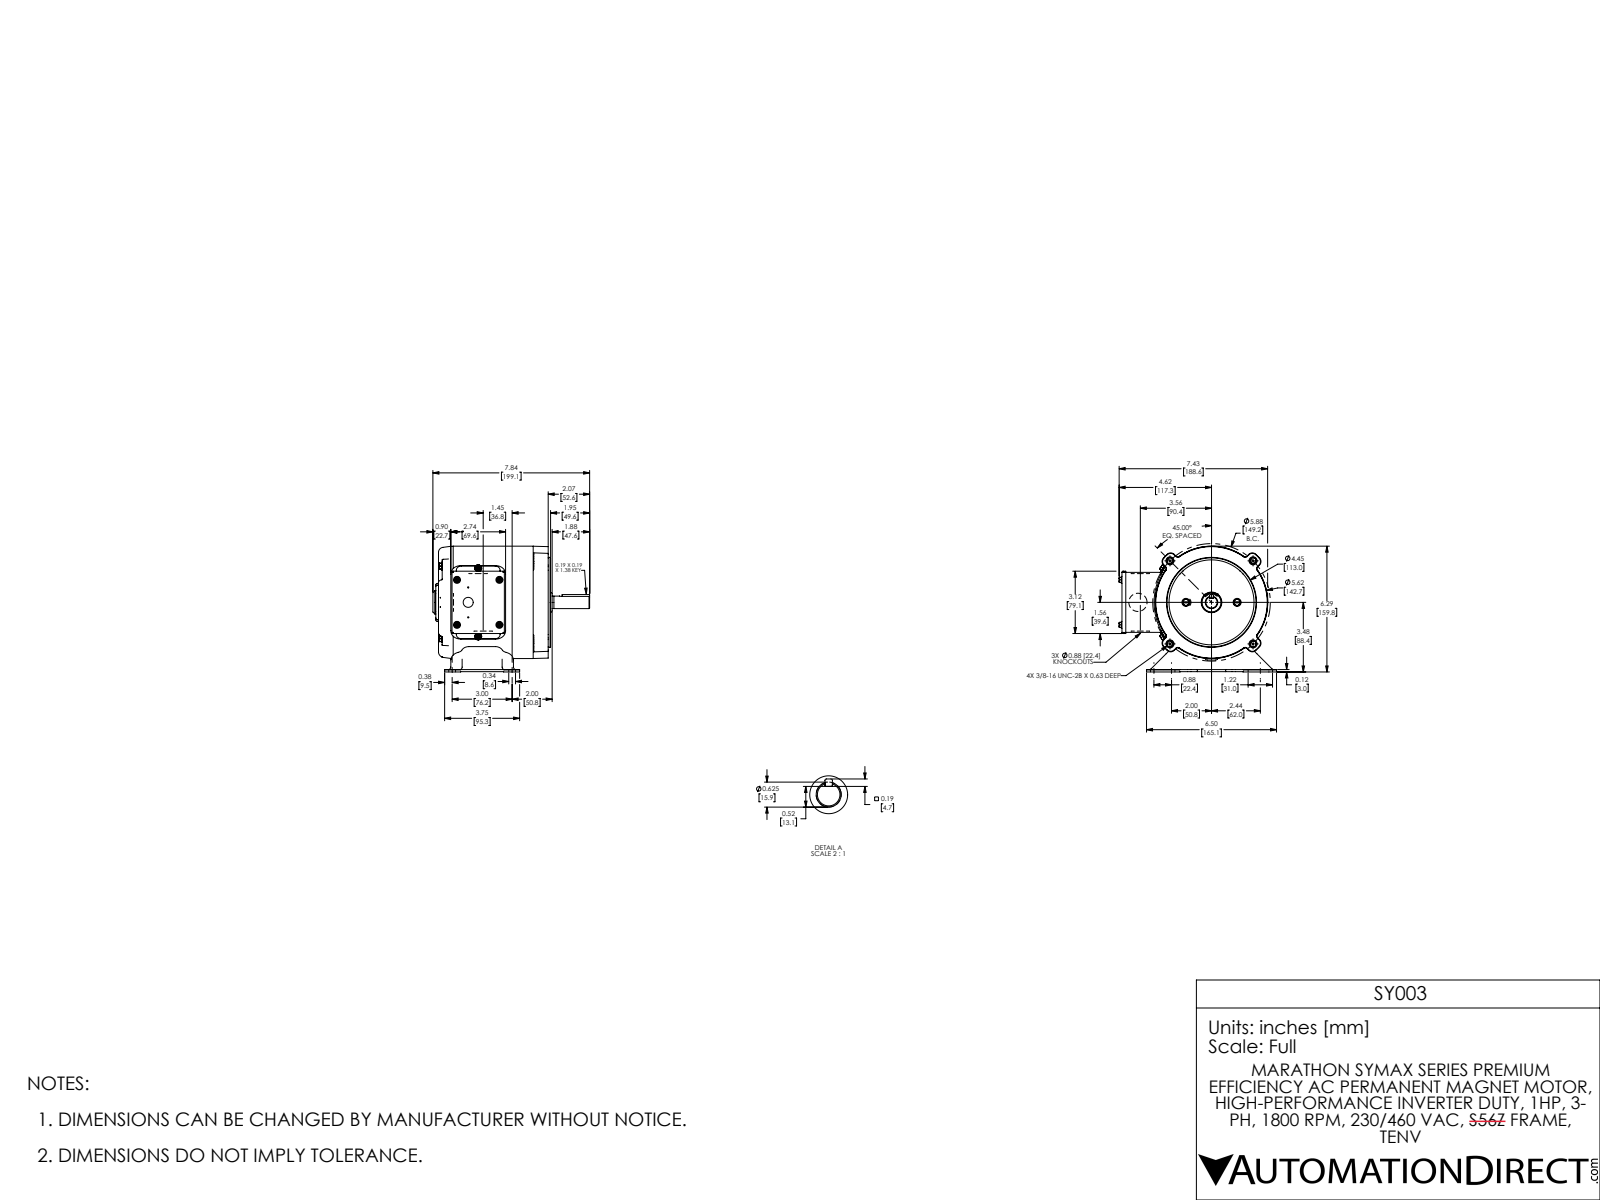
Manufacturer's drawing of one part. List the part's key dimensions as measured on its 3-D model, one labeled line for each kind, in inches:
Part name (STEP PRODUCT): 614-0004-003_RevE_56Z_1HP r1 Coord
STEP written by: SolidWorks 2017 (AUTOMOTIVE_DESIGN)
Units: inches
Bodies: 25 solids, 4169 faces (1801 planar, 576 cylindrical, 1792 other)
Overall size (bounding box): 8.837 × 7.869 × 6.29
Volume: 30.39 in³ · Surface area: 577.4 in²
Round holes (diameter × count): ⌀0.22 ×6, ⌀0.19 ×5, ⌀0.06 ×4, ⌀0.136 ×4, ⌀0.201 ×4, ⌀0.25 ×4, ⌀0.88 ×3, ⌀0.154 ×2, ⌀0.226 ×2, ⌀0.28 ×2, ⌀0.5 ×1, ⌀0.67 ×1
Round bosses / shafts (diameter × count): ⌀0.399 ×6, ⌀0.348 ×6, ⌀0.19 ×6, ⌀0.164 ×6, ⌀0.166 ×4, ⌀0.91 ×3, ⌀5.62 ×1, ⌀5.497 ×1
Partial cylindrical surfaces — rounded edges, fillets, slot ends (radius × count): R0.06 ×54, R0.045 ×40, R0.03 ×32, R0.13 ×22, R0.17 ×18, R0.25 ×14, R0.16 ×12, R0.38 ×12
Main face-to-face distances: 0.048, 0.09, 6.485, 6.395, 0.104, 2.452, 0.015, 2.952, 5.75, 0.13
Hole centre spacings: 2.12, 3.091, 1.893, 2.25, 2.562, 3.624, 4.548, 0.75
